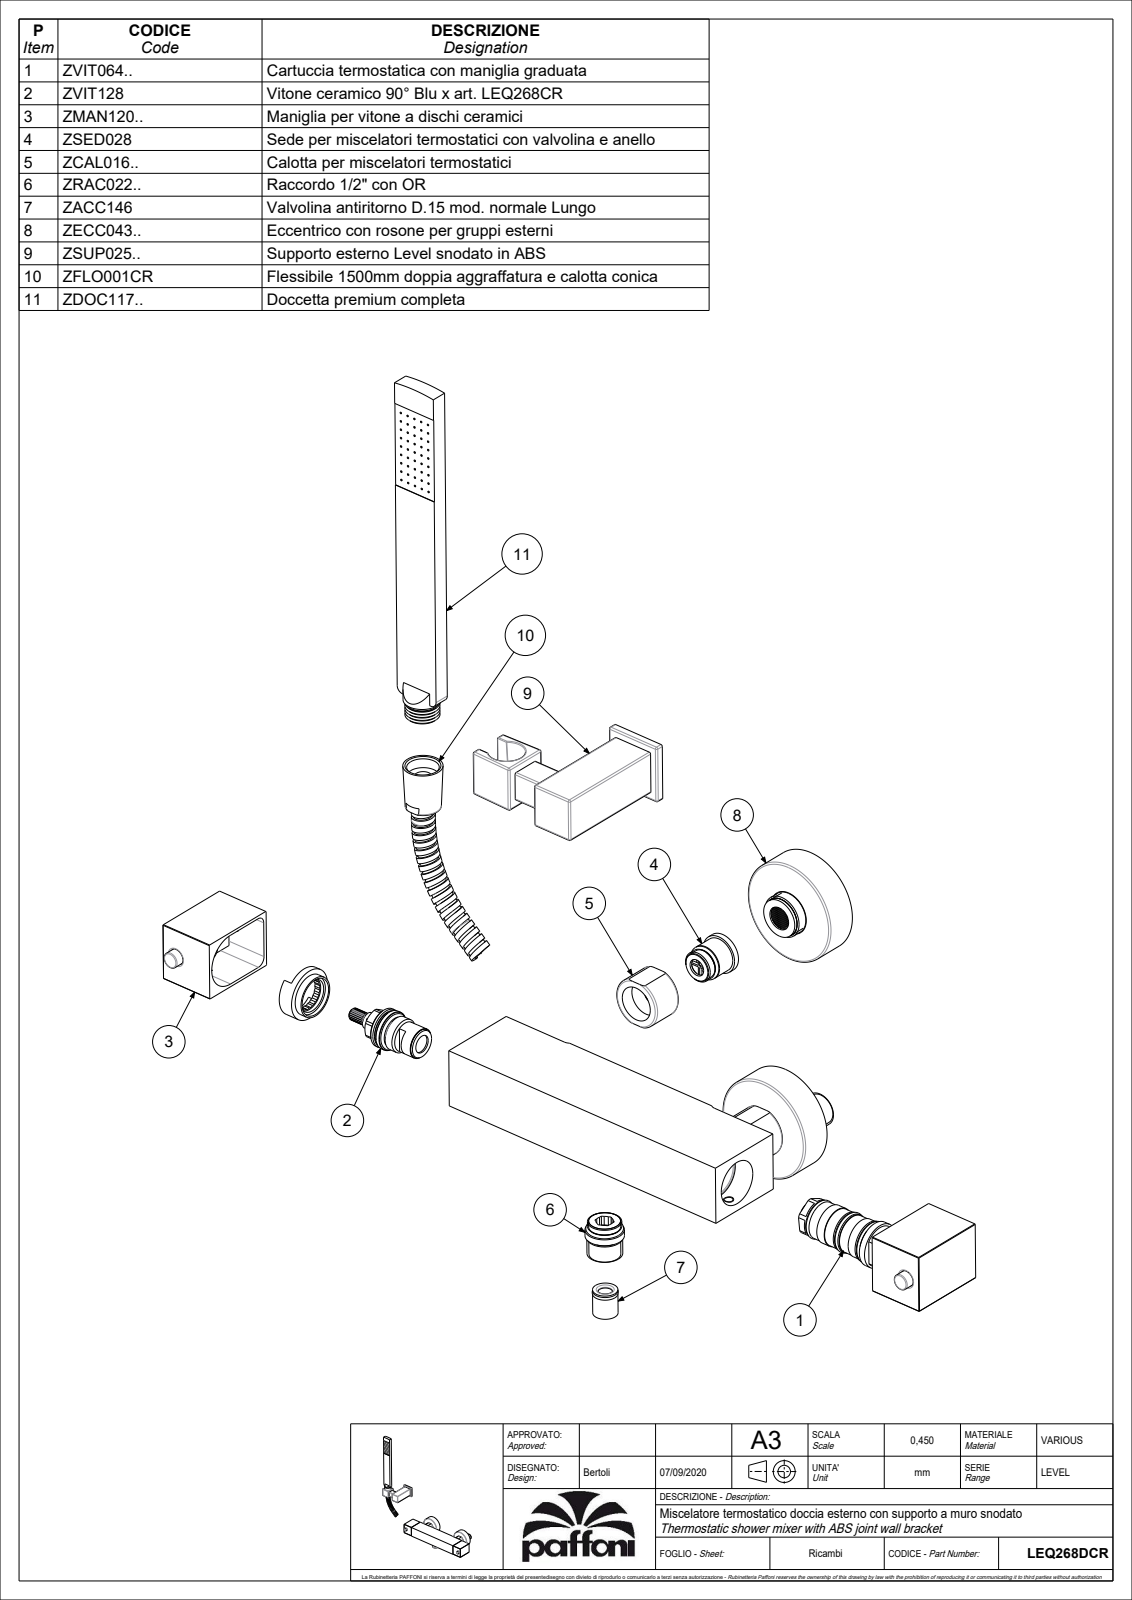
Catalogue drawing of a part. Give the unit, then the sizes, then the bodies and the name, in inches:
Units: inches
Overall size (bounding box): 18.037 × 14.587 × 3.907
Round holes (diameter × count): ⌀0.594 ×2, ⌀0.63 ×2, ⌀0.709 ×2, ⌀0.949 ×2, ⌀0.098 ×1, ⌀0.118 ×1, ⌀0.128 ×1, ⌀0.157 ×1, ⌀0.177 ×1, ⌀0.217 ×1, ⌀0.236 ×1, ⌀0.252 ×1
Round bosses / shafts (diameter × count): ⌀2.5 ×2, ⌀0.945 ×2, ⌀0.835 ×2, ⌀0.386 ×2, ⌀0.299 ×2, ⌀0.906 ×1, ⌀0.886 ×1, ⌀0.823 ×1
Partial cylindrical surfaces — rounded edges, fillets, slot ends (radius × count): R0.039 ×32, R0.02 ×6, R0.197 ×6, R0.069 ×2, R0.157 ×2, R0.614 ×2, R0.19 ×1, R0.65 ×1
Main face-to-face distances: 1.476, 3.728, 0.016, 1.461, 0.787, 2.116, 1.612, 1.329, 2.941, 2.047
Hole centre spacings: 0.157, 0.553, 1.994, 2.152, 5.906, 7.9, 8.057
Volume: 49.3 in³ · Surface area: 217.4 in²
Bodies: 5 solids, 525 faces (246 planar, 142 cylindrical, 137 other)
Part name (STEP PRODUCT): LEQ268DCR
STEP written by: CREO PARAMETRIC BY PTC INC, 2020044 (CONFIG_CONTROL_DESIGN)
